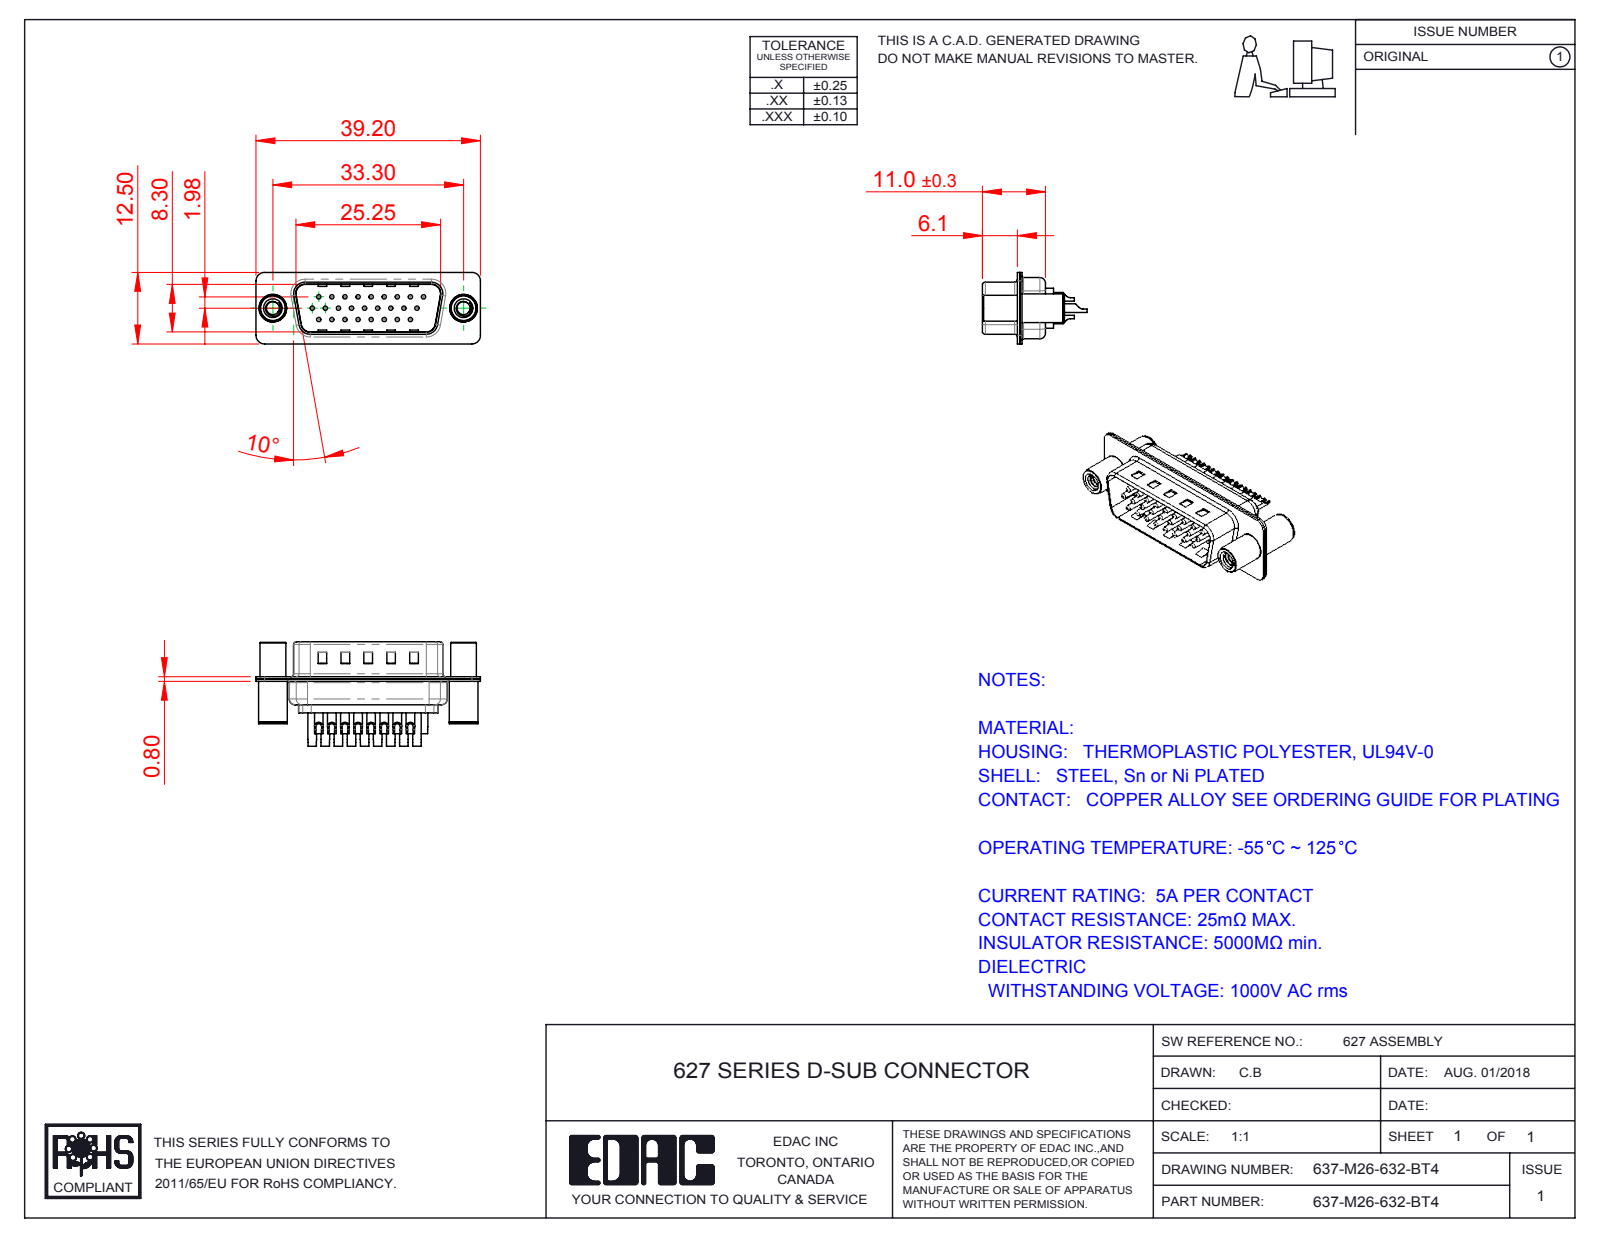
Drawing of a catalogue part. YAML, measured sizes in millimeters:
part_name: "637-M26-632-BT4; 637M Contact Row 3_32; 637M 4-40 Threaded Standoff and Board Spacer; 637M Contact Row 2_32 (+4 more)"
step_written_by: "SolidWorks 2016 (CONFIG_CONTROL_DESIGN)"
units: millimeters
bodies: {solids: 31, faces: 1388, planar: 379, cylindrical: 601, other: 408}
overall_size: [39.2, 18.25, 12.5]
volume: 2283
surface_area: 6602
round_holes:
  - {diameter: 0.75, count: 26}
  - {diameter: 1, count: 26}
  - {diameter: 1.6, count: 26}
  - {diameter: 2, count: 26}
  - {diameter: 2.26, count: 2}
  - {diameter: 3.26, count: 2}
  - {diameter: 4, count: 2}
  - {diameter: 4.8, count: 2}
round_bosses_or_shafts:
  - {diameter: 1.5, count: 26}
  - {diameter: 5, count: 2}
  - {diameter: 4.9, count: 2}
  - {diameter: 4.5, count: 2}
partial_cylinders:
  - {radius: 1.5, count: 16}
  - {radius: 2, count: 12}
  - {radius: 0.5, count: 8}
  - {radius: 1.6, count: 8}
  - {radius: 1, count: 7}
  - {radius: 0.25, count: 4}
  - {radius: 0.6, count: 4}
  - {radius: 0.65, count: 4}
face_to_face_distances: [0.4, 0.8, 9.5, 9.1, 8.7, 9.9, 0.75, 0.35, 1.2, 1.9]
hole_center_spacings: [3.96, 2.28, 4.57, 6.05, 2.29, 8.24, 6.86, 10.48]
